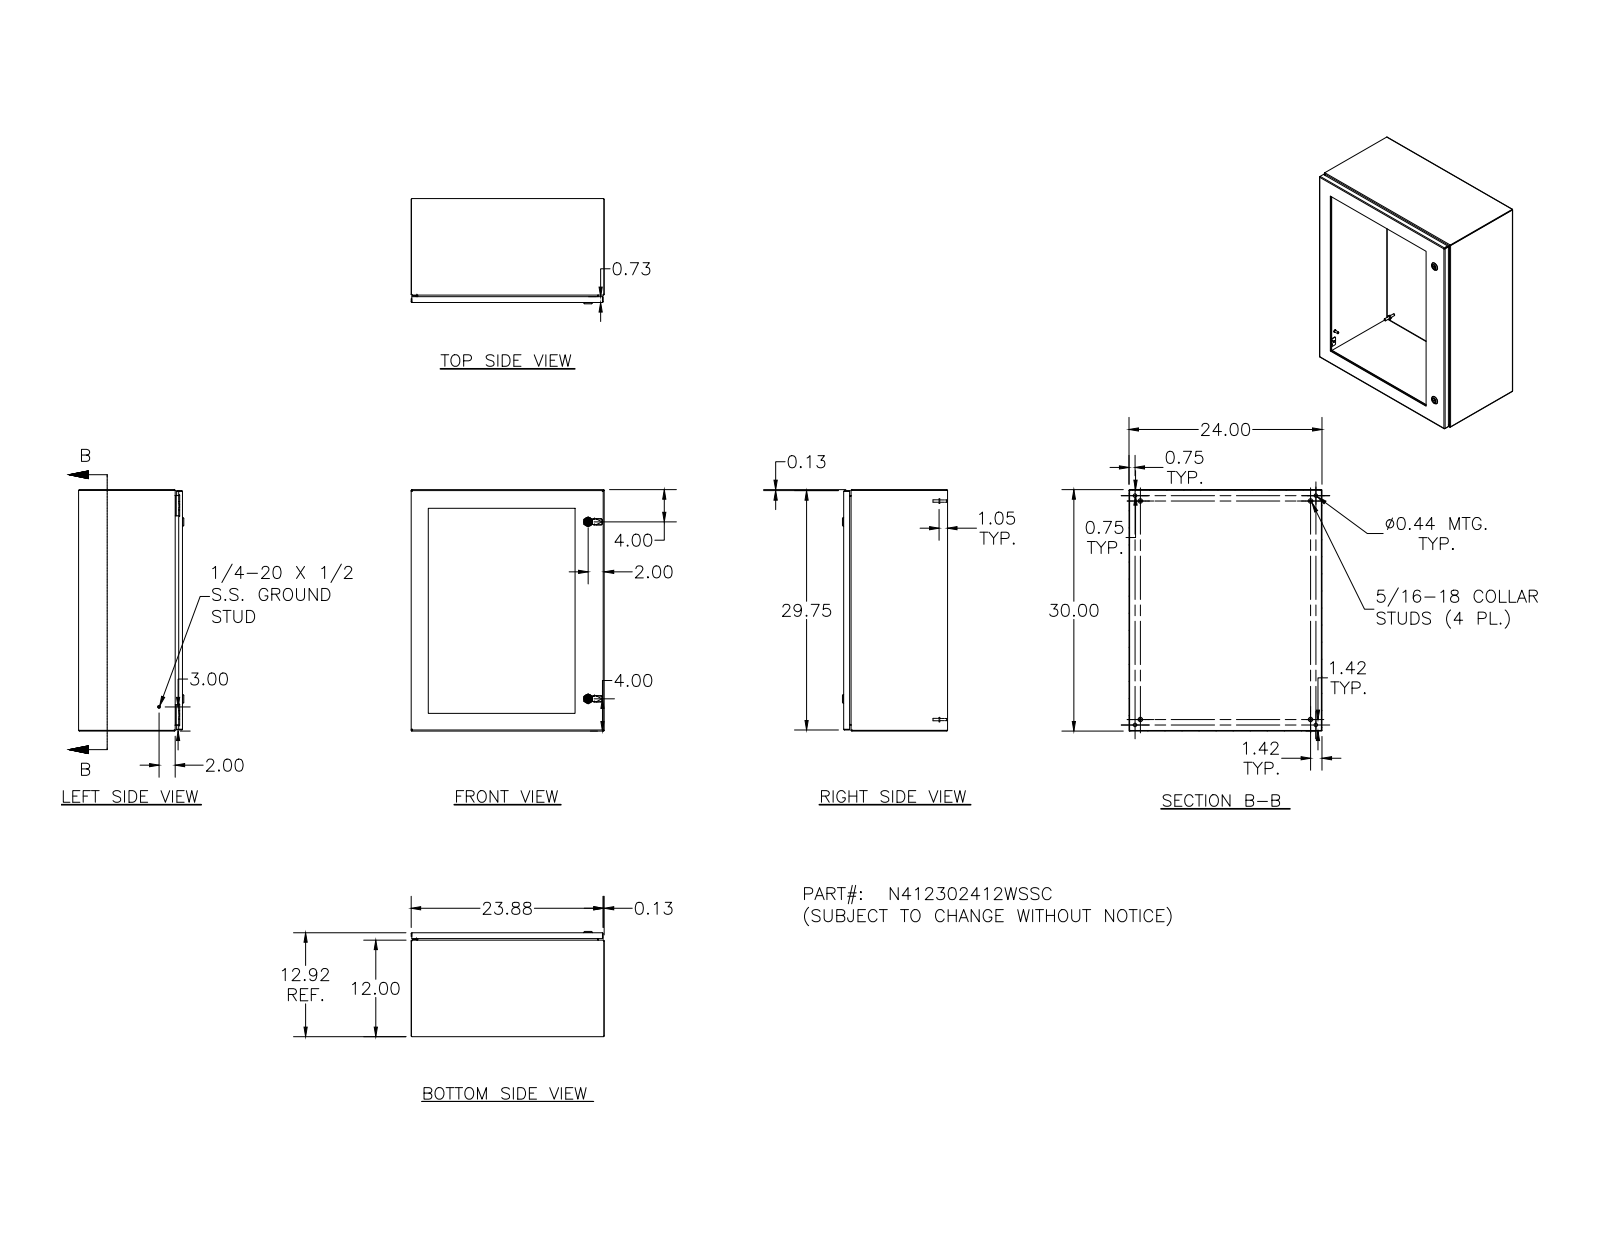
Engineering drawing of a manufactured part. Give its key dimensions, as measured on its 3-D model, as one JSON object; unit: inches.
{"part_name": "N412302412WSSC; N412302412WSSCBKP; N4123024WSSCLID; HFW328176 (+8 more)", "step_written_by": "Autodesk Inventor 2011 (AUTOMOTIVE_DESIGN)", "units": "inches", "bodies": {"solids": 94, "faces": 2494, "planar": 1017, "cylindrical": 688, "other": 789}, "overall_size": [30, 24, 13.075], "volume_in3": 319.6, "surface_area_in2": 6279, "round_holes": [[0.156, 26], [0.281, 24], [0.093, 4], [0.152, 4], [0.167, 4], [0.172, 4], [0.188, 4], [0.437, 4], [0.197, 2], [0.315, 2], [0.394, 2], [0.402, 2]], "round_bosses_or_shafts": [[0.19, 24], [0.253, 23], [0.25, 10], [0.563, 4], [0.36, 4], [0.32, 4], [0.3, 4], [0.275, 4]], "partial_cylinders_radius": [[0.031, 34], [0.05, 26], [0.105, 24], [0.016, 18], [0.125, 16], [0.02, 15], [0.032, 8], [0.157, 8]], "face_to_face_distances": [0.074, 12.843, 12.769, 23.926, 29.926, 0.25, 12.593, 12.519, 23.852, 24], "hole_center_spacings": [4, 8, 12, 27.047, 26, 27.92, 16, 26.75]}
